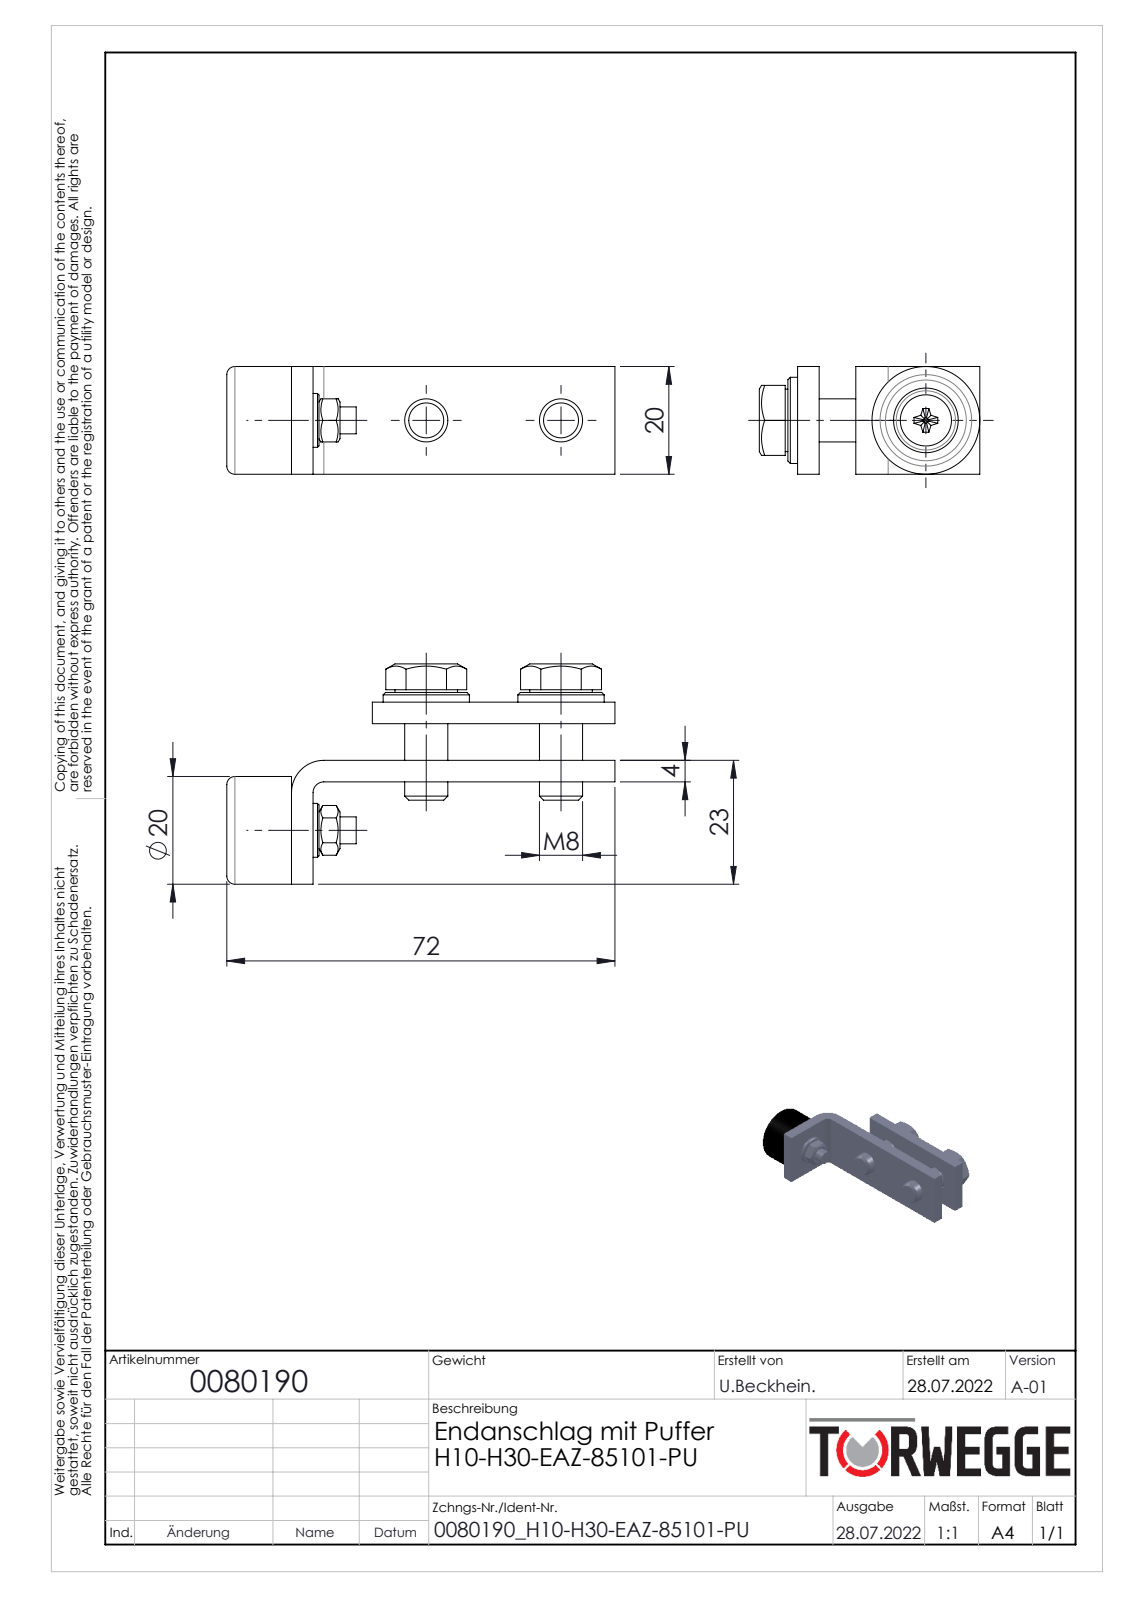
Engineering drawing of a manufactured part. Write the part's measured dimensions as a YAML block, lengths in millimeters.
part_name: "0080190"
step_written_by: "SolidWorks 2020 (AUTOMOTIVE_DESIGN)"
units: millimeters
bodies: {solids: 10, faces: 146, planar: 67, cylindrical: 46, other: 33}
overall_size: [72, 40.9, 20]
volume: 16354
surface_area: 11538
round_holes:
  - {diameter: 6.4, count: 2}
  - {diameter: 8.4, count: 2}
  - {diameter: 9, count: 2}
  - {diameter: 4.13, count: 1}
  - {diameter: 5.3, count: 1}
  - {diameter: 5.5, count: 1}
  - {diameter: 5.8, count: 1}
  - {diameter: 12, count: 1}
round_bosses_or_shafts:
  - {diameter: 16, count: 2}
  - {diameter: 11.6, count: 2}
  - {diameter: 8, count: 2}
  - {diameter: 20, count: 1}
  - {diameter: 10, count: 1}
  - {diameter: 9.5, count: 1}
  - {diameter: 5, count: 1}
partial_cylinders:
  - {radius: 2, count: 1}
  - {radius: 6, count: 1}
face_to_face_distances: [4, 10.8, 14.8, 6.8, 20, 1.8, 5.8, 12.6, 16.6, 8]
hole_center_spacings: [25]
